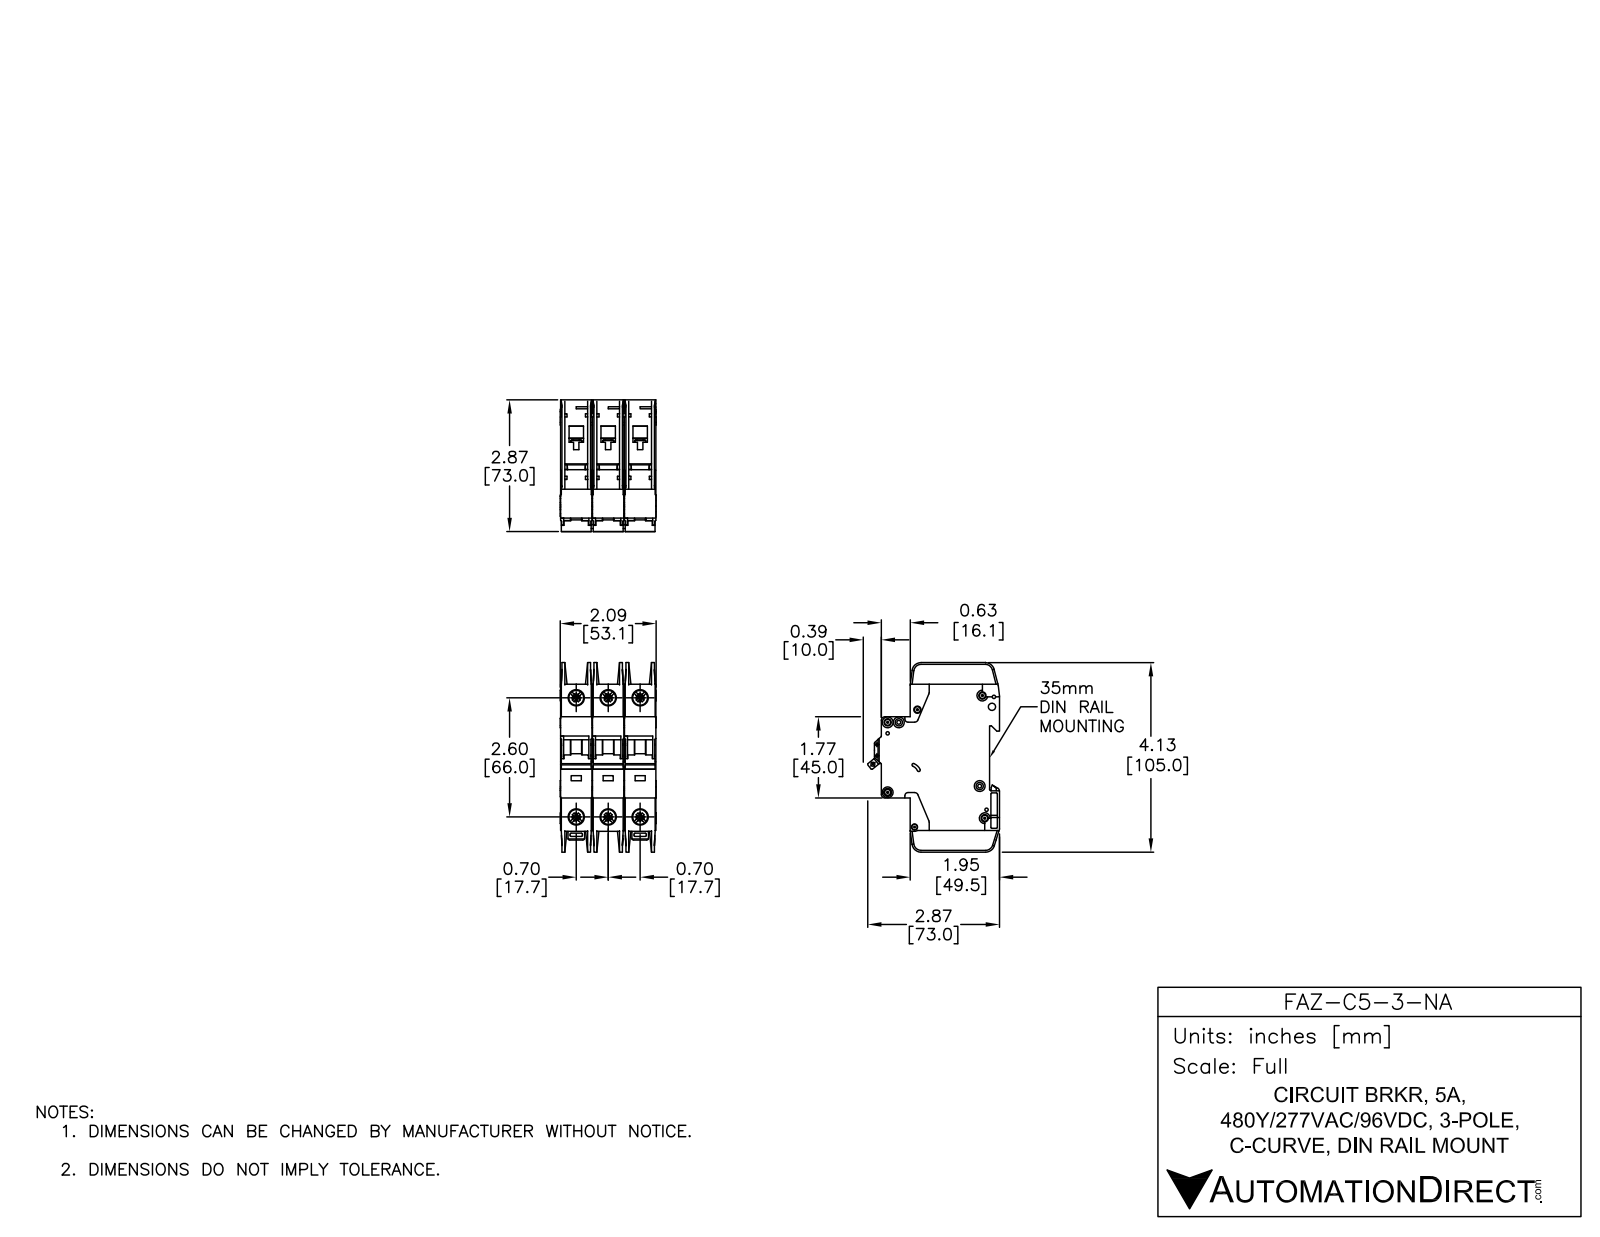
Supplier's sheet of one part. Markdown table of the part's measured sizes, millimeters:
| quantity | value |
| --- | --- |
| part name | FAZ-C5-3-NA |
| STEP written by | SolidWorks 2014 (AUTOMOTIVE_DESIGN) |
| units | millimeters |
| bodies | 9 solids, 2352 faces (1227 planar, 789 cylindrical, 336 other) |
| overall size | 105 × 73.04 × 53.1 |
| volume | 233 085 mm³ |
| surface area | 74 219 mm² |
| round holes (diameter × count) | 3.6 × 7, 7.15 × 6, 8.2 × 6, 1.09 × 2, 1.5 × 2, 4 × 2, 1.9 × 1, 2.15 × 1, 2.2 × 1, 2.55 × 1, 3.3 × 1, 3.4 × 1 |
| round bosses / shafts (diameter × count) | 6 × 7, 2.5 × 3 |
| partial cylindrical surfaces (radius × count) | 0.25 × 65, 0.5 × 30, 1 × 26, 2 × 14, 1.8 × 5, 5 × 5, 4 × 4, 0.2 × 2 |
| main face-to-face distances | 17.7, 35.4, 17.5, 35.2, 0.7, 15.05, 2.45, 1.75, 15.75, 13.3 |
| hole center spacings | 17.7, 68.33, 66, 6.2, 35.4, 74.89, 5.19, 6.1 |
